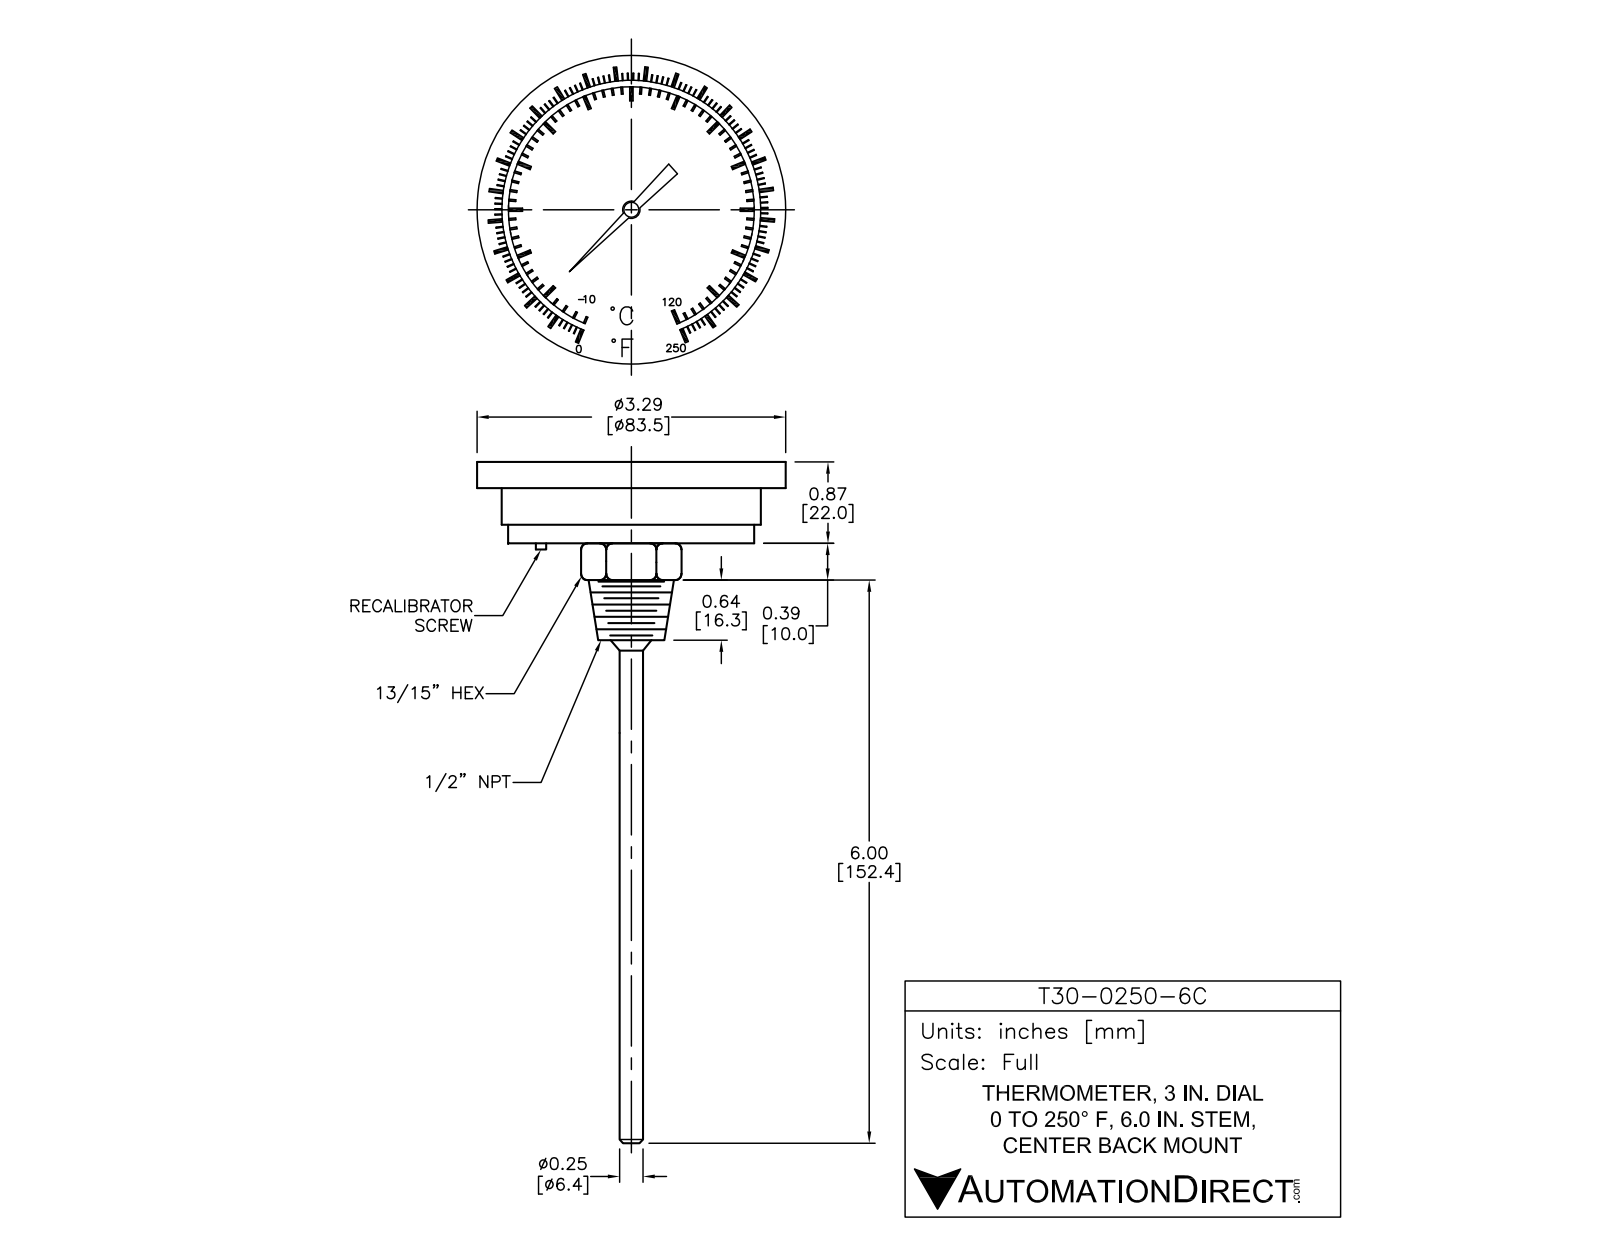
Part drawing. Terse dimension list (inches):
name: T30-0250-6C
written by: SolidWorks 2021 (AUTOMOTIVE_DESIGN)
unit: in
bodies: 73 solids, 1252 faces (1096 planar, 85 cylindrical, 71 other)
size: 7.26 × 3.29 × 3.29
volume: 3.256 in³; area: 35.86 in²
holes: 1× ⌀0.067, 1× ⌀2.69
bosses: 1× ⌀3.29, 1× ⌀2.76, 1× ⌀2.62, 1× ⌀0.846, 1× ⌀0.258
rounds: 1× R0.04, 1× R0.709, 1× R0.859, 1× R0.969, 1× R1.119
face distances: 0.222, 0.078, 0.3, 0.87, 0.648, 0.57, 0.59, 0.368, 0.29, 0.28
